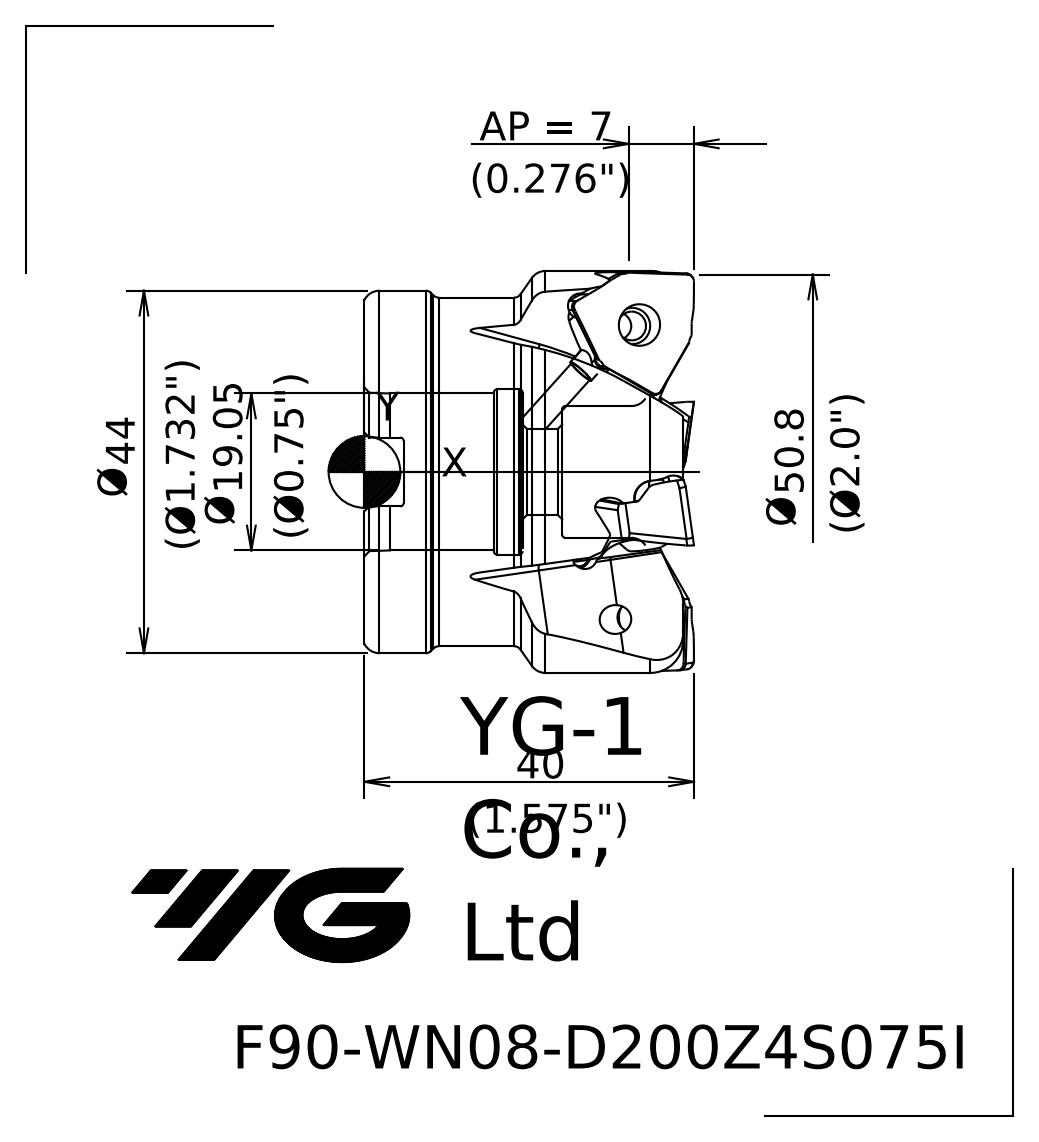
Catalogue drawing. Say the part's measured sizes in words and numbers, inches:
The part is named "10223F5CCA8Abcfi". Its 3-D file was written by "SIEMENS PLM Software NX 10.0 (AP203_CONFIGURATION_CONTROLLED_3D_DESIGN_OF_MECHANICAL_PARTS_AND_ASSEMBLIES_MIM_LF)". It is 1 solid with 88 faces: 16 planar, 11 cylindrical and 61 other. Overall it measures 2 by 2 by 1.575 inches. Its volume is 3.178 cubic inches and its surface area 25.02 square inches. Round holes: 1 of diameter 0.413, 1 of diameter 0.63, 1 of diameter 0.75, 1 of diameter 0.789. Round bosses or shafts: 1 of diameter 1.921, 1 of diameter 1.732, 1 of diameter 1.665. Partial cylindrical surfaces (rounded edges, fillets, slot ends): 2 of radius 0.016. The main face-to-face distances are 1.524, 1.337, 0.187, 0.768, 0.569, 0.756, 0.329, 0.579, 0.189, 0.758.
